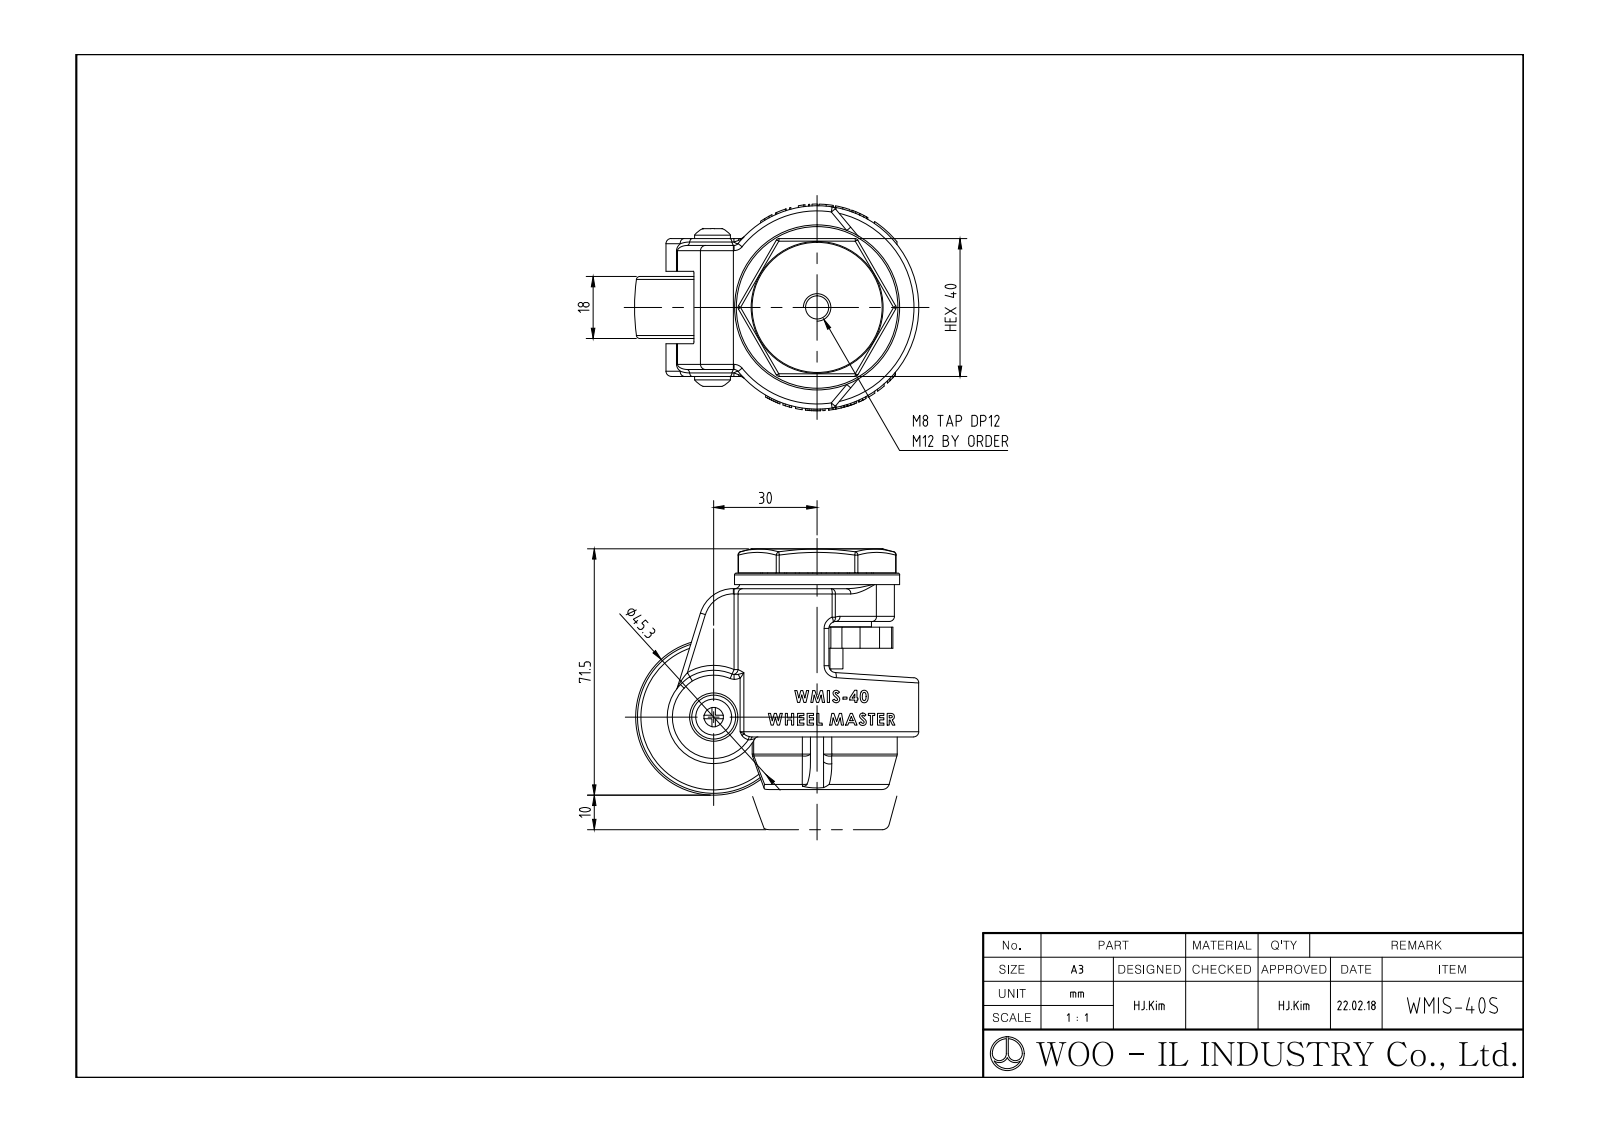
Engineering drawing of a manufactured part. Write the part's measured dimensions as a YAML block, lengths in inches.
part_name: "WMIS-40S"
step_written_by: "SolidWorks 2019 (AUTOMOTIVE_DESIGN)"
units: inches
bodies: {solids: 1, faces: 678, planar: 324, cylindrical: 153, other: 201}
overall_size: [3.215, 2.815, 2.362]
volume: 8.788
surface_area: 55.64
round_holes:
  - {diameter: 0.208, count: 1}
  - {diameter: 0.264, count: 1}
  - {diameter: 0.472, count: 1}
  - {diameter: 0.551, count: 1}
  - {diameter: 0.827, count: 1}
  - {diameter: 1.882, count: 1}
round_bosses_or_shafts:
  - {diameter: 1.85, count: 1}
  - {diameter: 1.811, count: 1}
  - {diameter: 0.343, count: 1}
  - {diameter: 0.257, count: 1}
  - {diameter: 0.236, count: 1}
partial_cylinders:
  - {radius: 0.059, count: 18}
  - {radius: 0.02, count: 16}
  - {radius: 0.039, count: 4}
  - {radius: 0.019, count: 2}
  - {radius: 0.079, count: 2}
  - {radius: 0.197, count: 2}
  - {radius: 0.394, count: 1}
  - {radius: 0.531, count: 1}
face_to_face_distances: [0.059, 0.709, 0.768, 1.181, 0.374, 1.468, 2.649, 1.58, 0.399, 1.069]
hole_center_spacings: [1.981]
